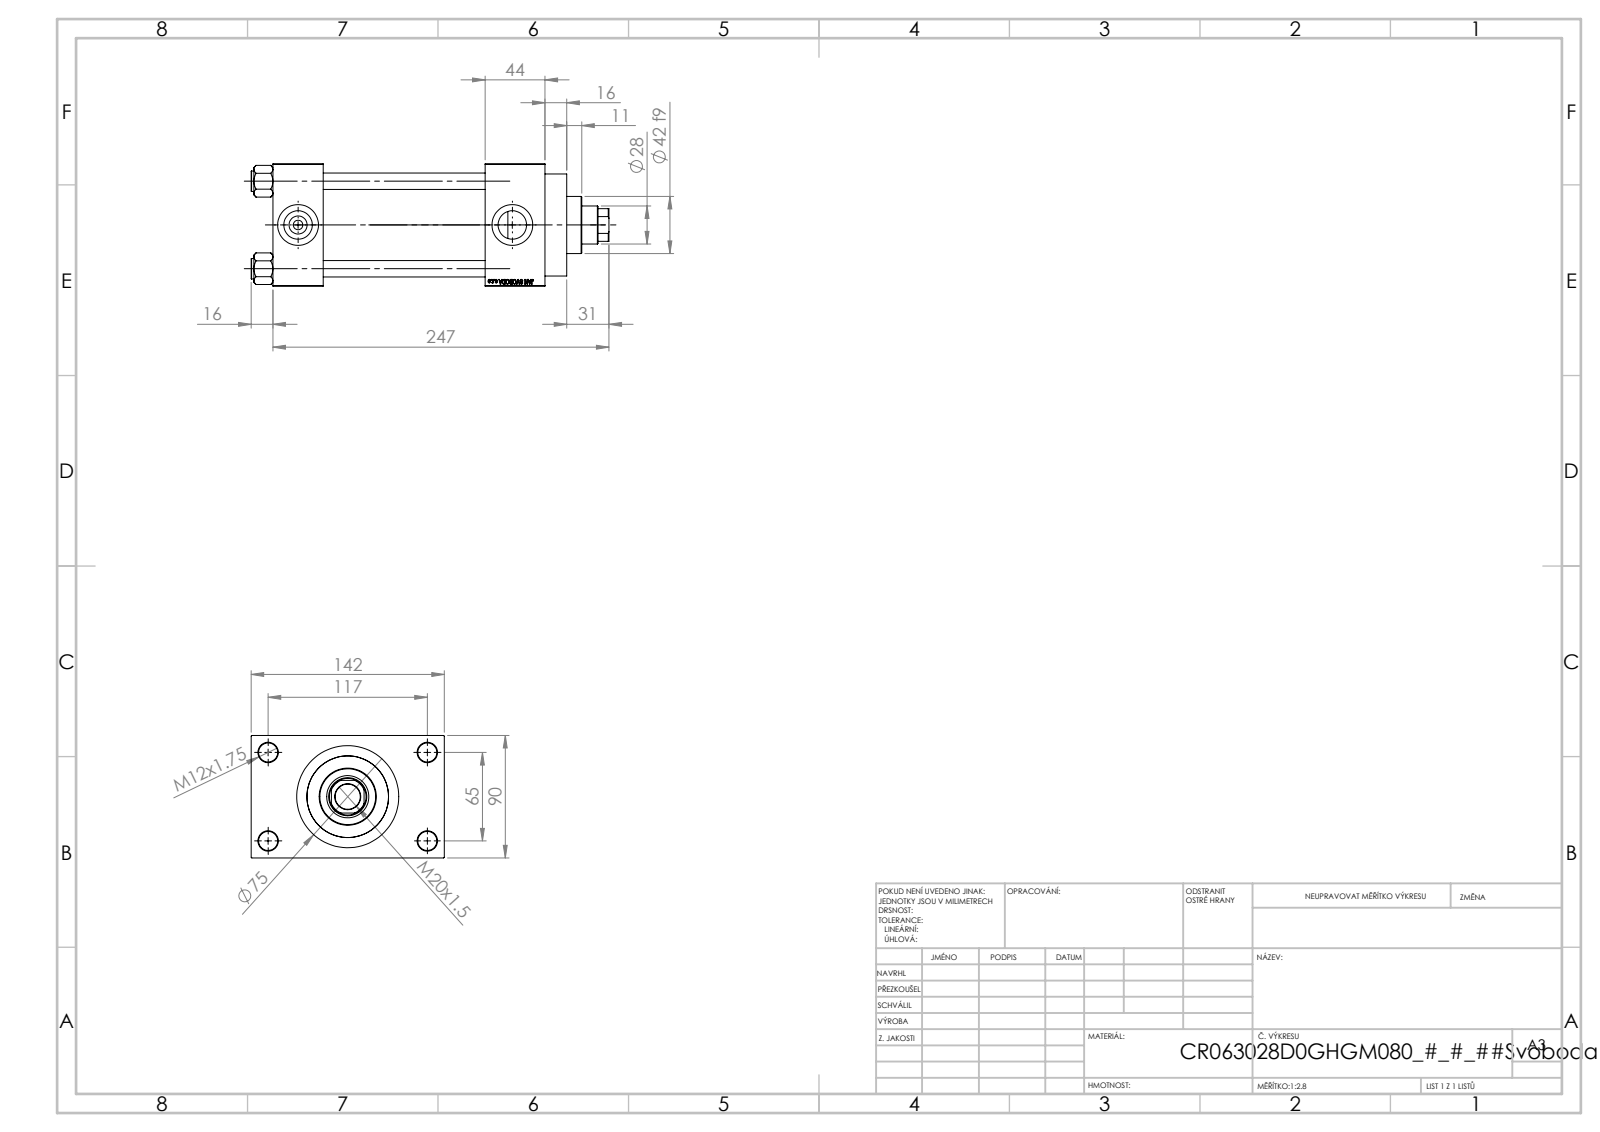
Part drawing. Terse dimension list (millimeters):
name: V215CR_D_TYCINKA; V215_VC_A; NUT_M5_D; V215CR_VCP_D (+1 more)
written by: SolidWorks 2019 (CONFIG_CONTROL_DESIGN)
unit: mm
bodies: 11 solids, 1103 faces (497 planar, 88 cylindrical, 518 other)
size: 263 × 142 × 90
volume: 1 198 000 mm³; area: 239 521 mm²
holes: 4× ⌀12, 4× ⌀14, 2× ⌀7, 2× ⌀20.96, 2× ⌀30, 1× ⌀18.5, 1× ⌀28, 1× ⌀31, 1× ⌀50, 1× ⌀60, 1× ⌀63
bosses: 4× ⌀15, 1× ⌀75, 1× ⌀69, 1× ⌀42
rounds: 1× R13.5
face distances: 90, 119, 37, 156, 163, 200, 44, 26, 116, 16
hole spacings: 26.35, 45.47, 64.3, 66.92, 69.81, 90.65, 111.34, 65
